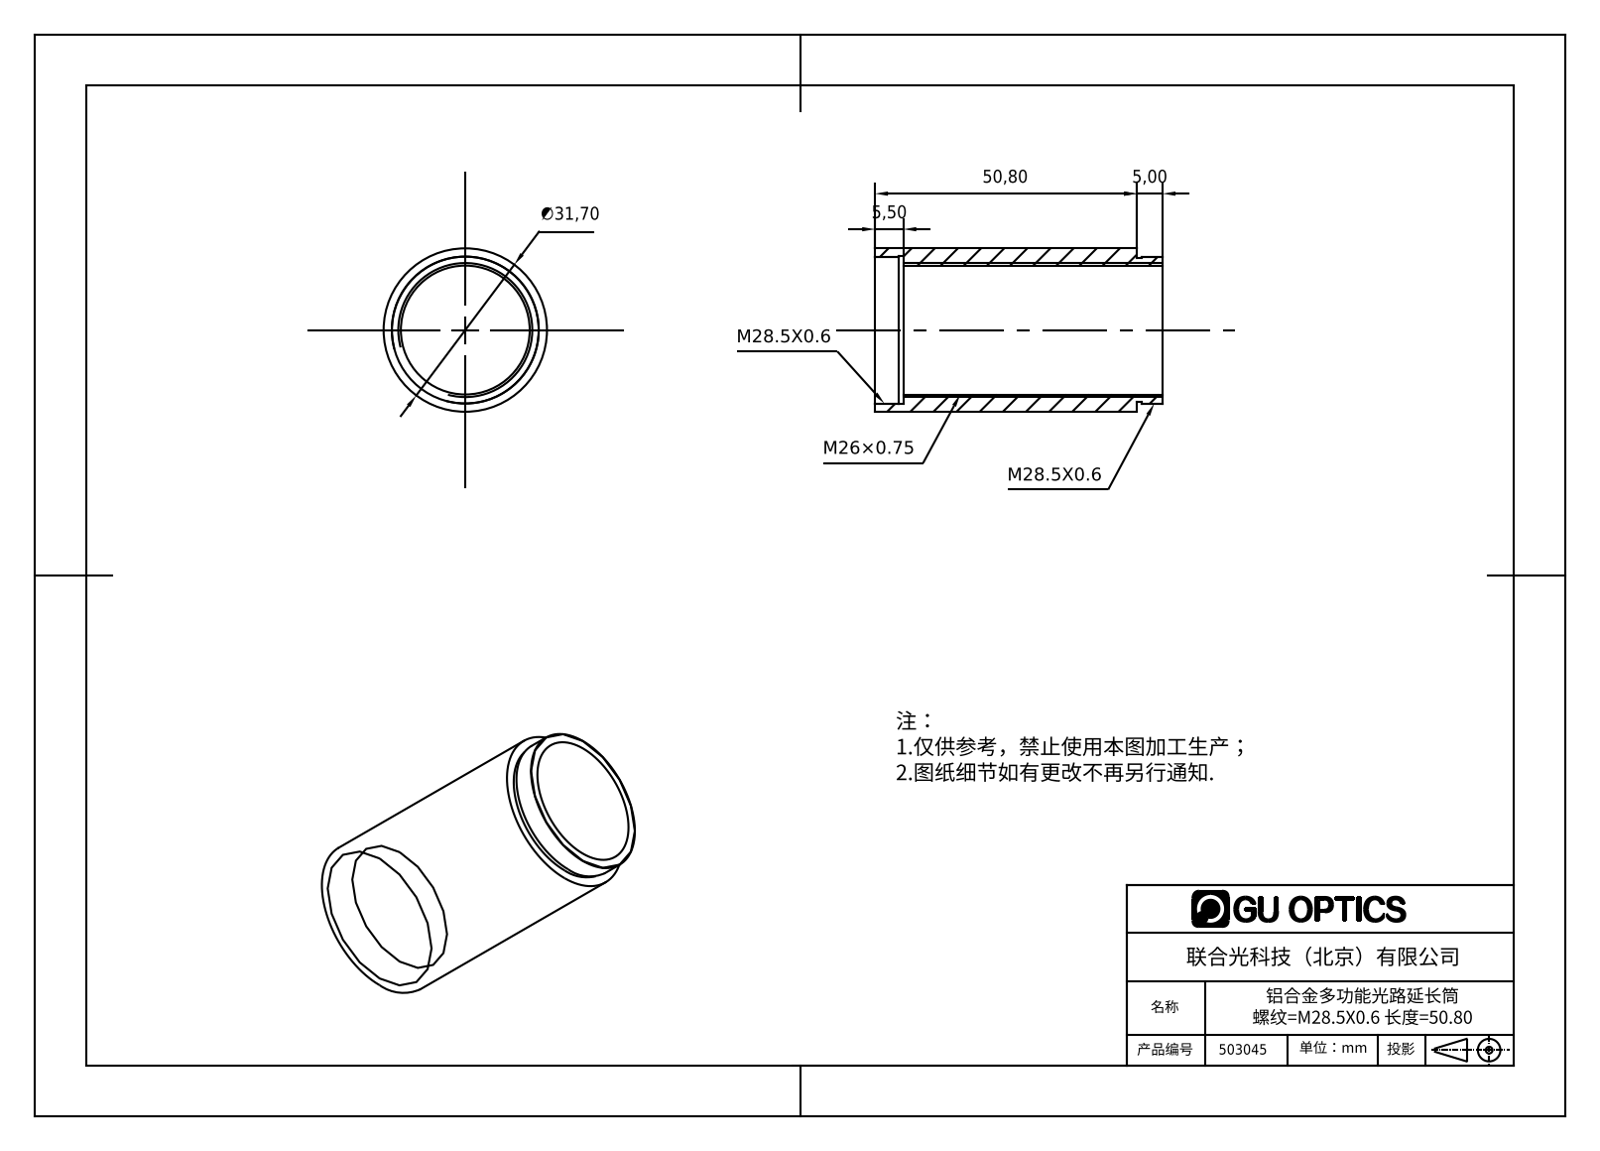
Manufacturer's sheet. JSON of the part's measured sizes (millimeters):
{"part_name": "503044", "step_written_by": "SolidWorks 2016 (AUTOMOTIVE_DESIGN)", "units": "millimeters", "bodies": {"solids": 1, "faces": 18, "planar": 6, "cylindrical": 12, "other": 0}, "overall_size": [55.8, 31.7, 31.7], "volume_mm3": 15052, "surface_area_mm2": 10608, "round_holes": [[25, 1], [28.5, 1], [28.7, 1]], "round_bosses_or_shafts": [[31.7, 1], [28, 1]], "face_to_face_distances": [45.3, 5.5, 50.8, 55.8, 50.3, 5, 1, 46.3, 51.8, 4]}
